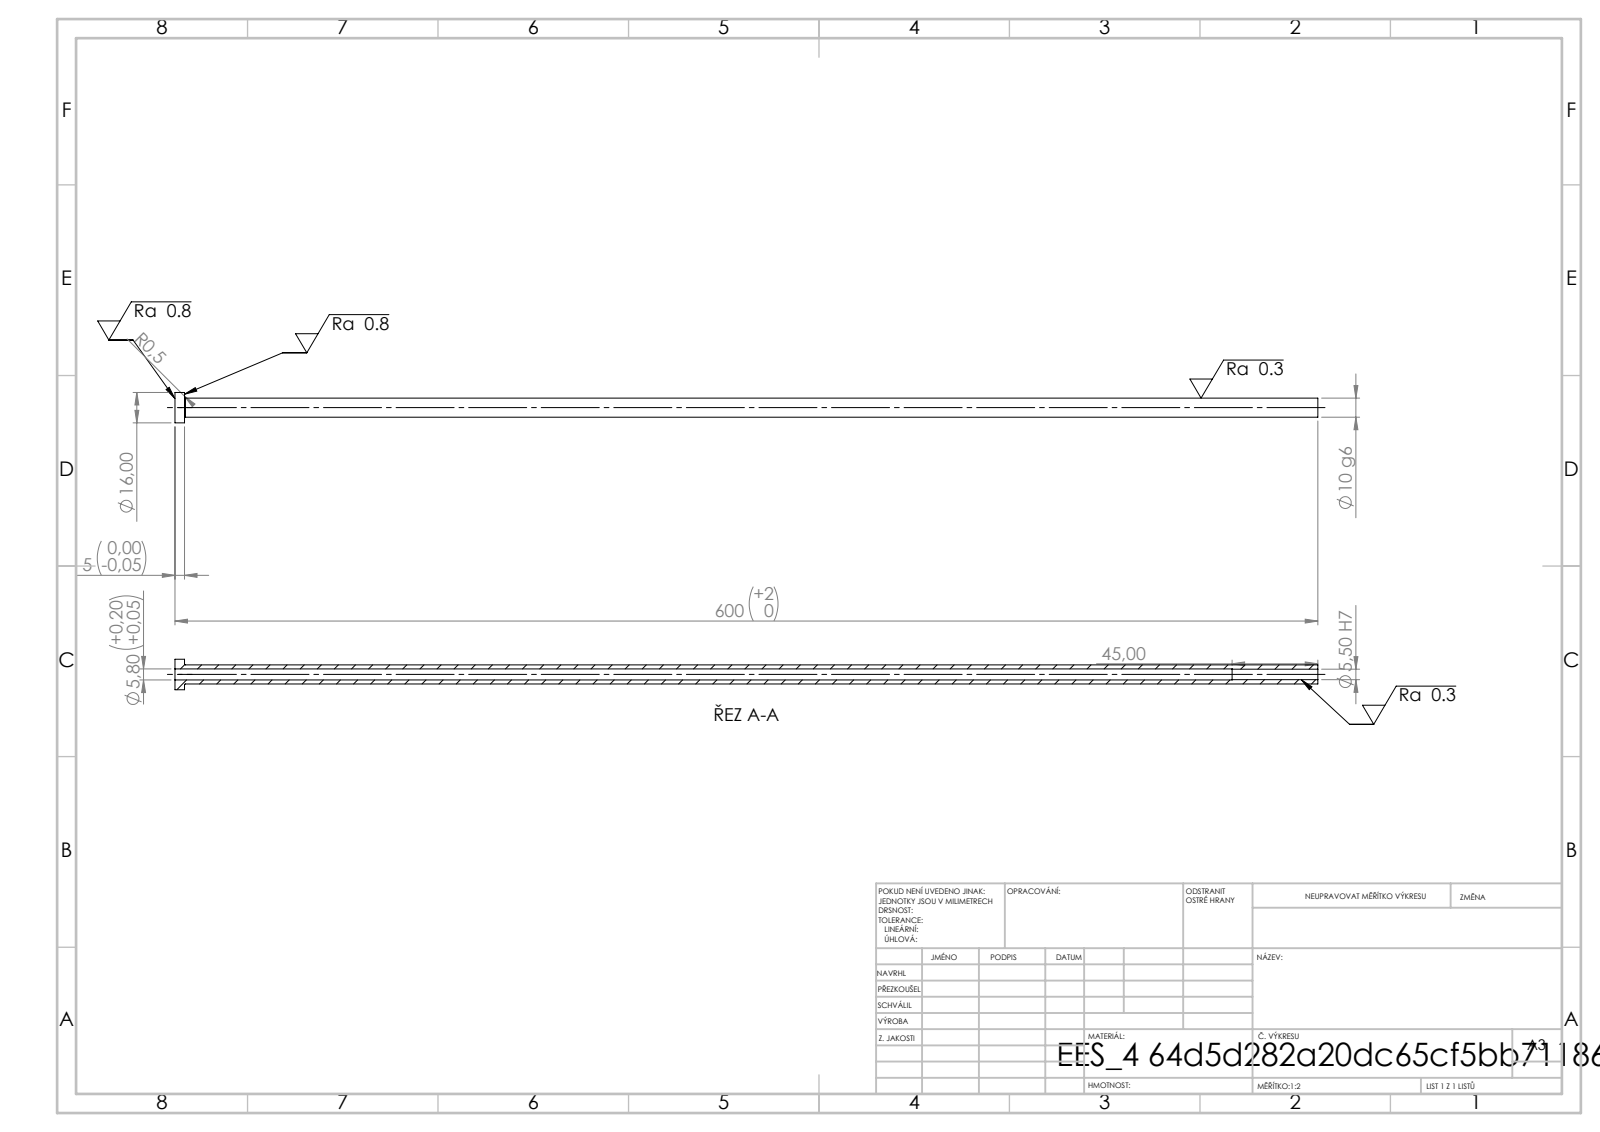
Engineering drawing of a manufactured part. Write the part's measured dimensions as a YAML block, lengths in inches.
step_written_by: "SolidWorks 2019 (CONFIG_CONTROL_DESIGN)"
units: inches
bodies: {solids: 1, faces: 14, planar: 4, cylindrical: 8, other: 2}
overall_size: [23.622, 0.63, 0.63]
volume: 1.953
surface_area: 46.78
round_holes:
  - {diameter: 0.217, count: 1}
  - {diameter: 0.228, count: 1}
round_bosses_or_shafts:
  - {diameter: 0.63, count: 1}
  - {diameter: 0.394, count: 1}
face_to_face_distances: [0.197, 23.622, 23.425, 21.85, 21.654, 1.772]
